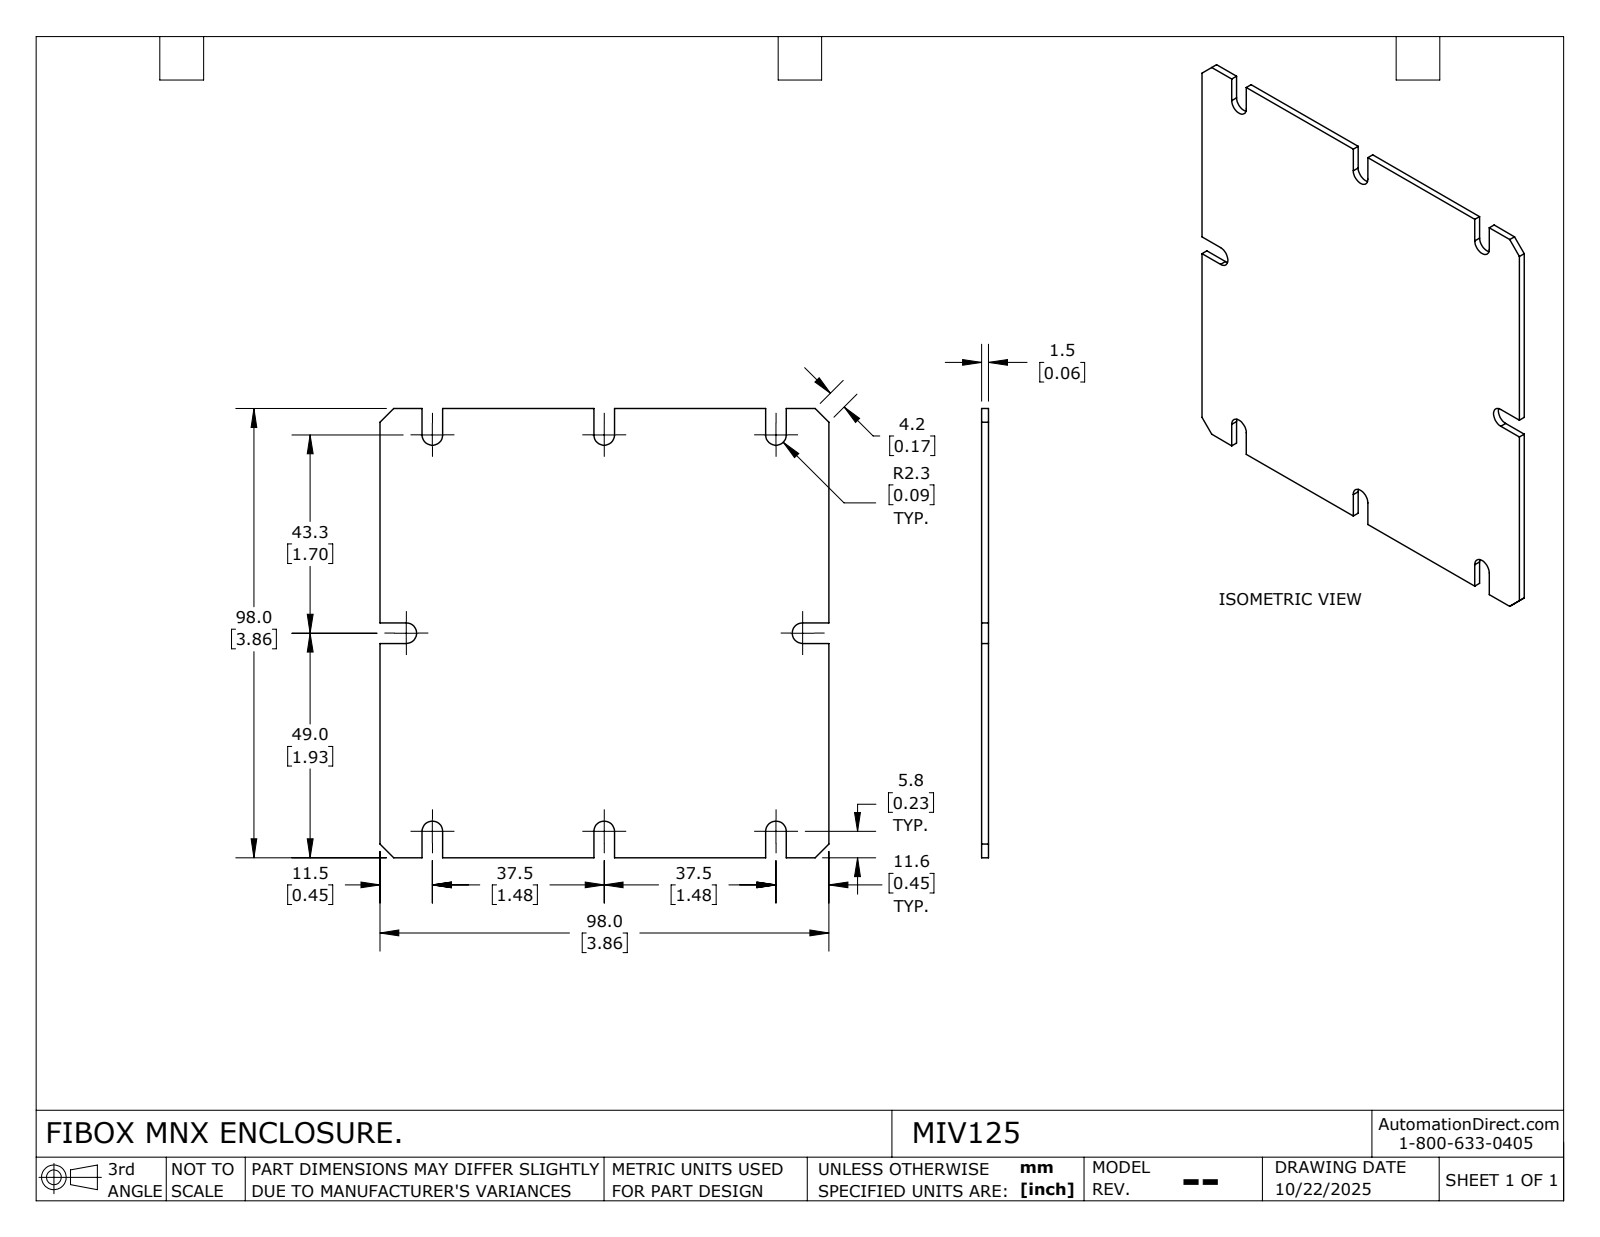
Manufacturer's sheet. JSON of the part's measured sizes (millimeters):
{"part_name": "MIV125_Default", "step_written_by": "SolidWorks 2024 (CONFIG_CONTROL_DESIGN)", "units": "millimeters", "bodies": {"solids": 1, "faces": 42, "planar": 34, "cylindrical": 8, "other": 0}, "overall_size": [98, 98, 1.5], "volume_mm3": 13973, "surface_area_mm2": 19377, "partial_cylinders_radius": [[2.25, 8]], "face_to_face_distances": [1.5, 98, 4.5, 37.5, 46.75, 51.25, 75, 33, 42, 84.2]}
